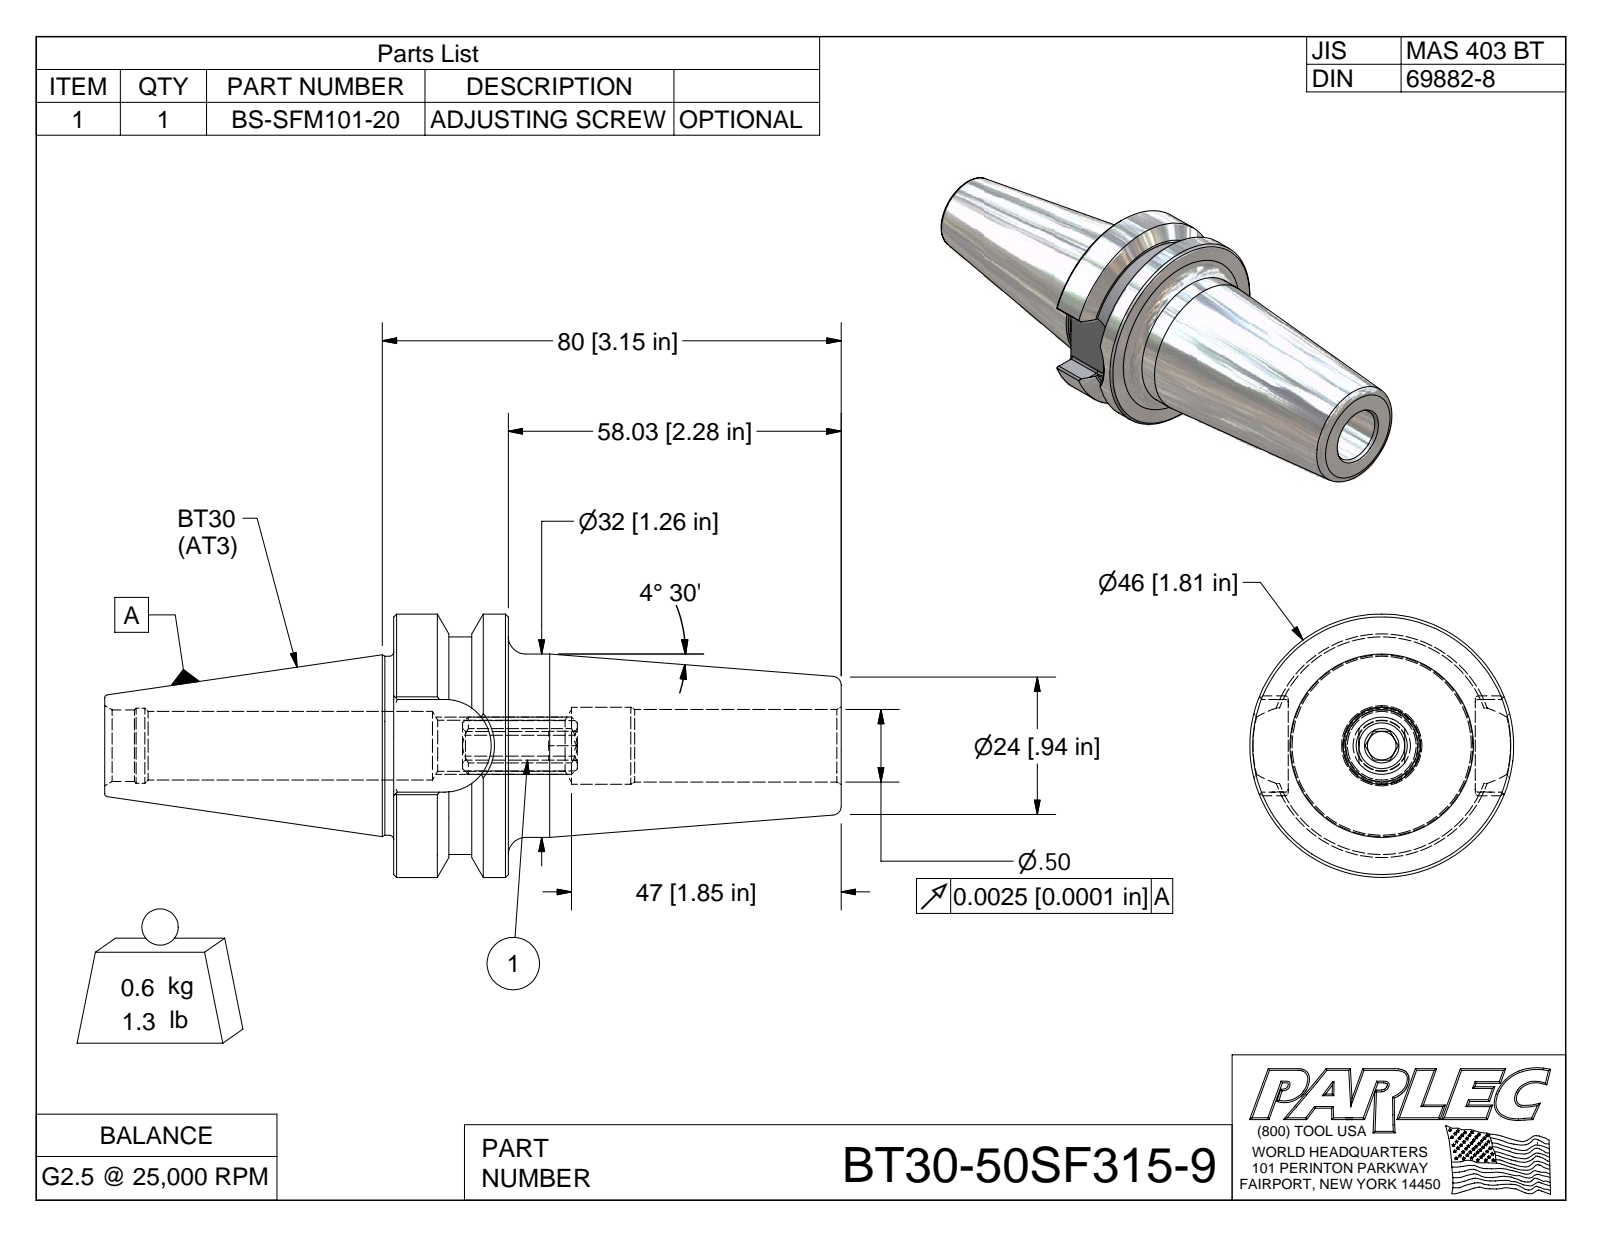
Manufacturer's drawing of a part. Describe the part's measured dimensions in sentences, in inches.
The part is named "BT30-50SF315-9; BT30-50SF315-9-1; BS-SFM101-20". Its 3-D file was written by "Autodesk Inventor 2009 (AUTOMOTIVE_DESIGN)". It is 2 solids with 92 faces: 35 planar, 22 cylindrical and 35 other. Overall it measures 5.056 by 1.811 by 1.811 inches. Its volume is 4.716 cubic inches and its surface area 31.5 square inches. Round holes: 1 of diameter 0.499, 1 of diameter 0.517, 1 of diameter 0.529. Round bosses or shafts: 1 of diameter 1.811, 1 of diameter 1.26, 1 of diameter 1.23. Partial cylindrical surfaces (rounded edges, fillets, slot ends): 8 of radius 0.02, 1 of radius 0.197, 1 of radius 0.319, 1 of radius 0.748. The main face-to-face distances are 0.787, 0.484, 0.799, 1.283, 3.072, 2.285, 0.315, 1.984, 2.771, 5.056.
